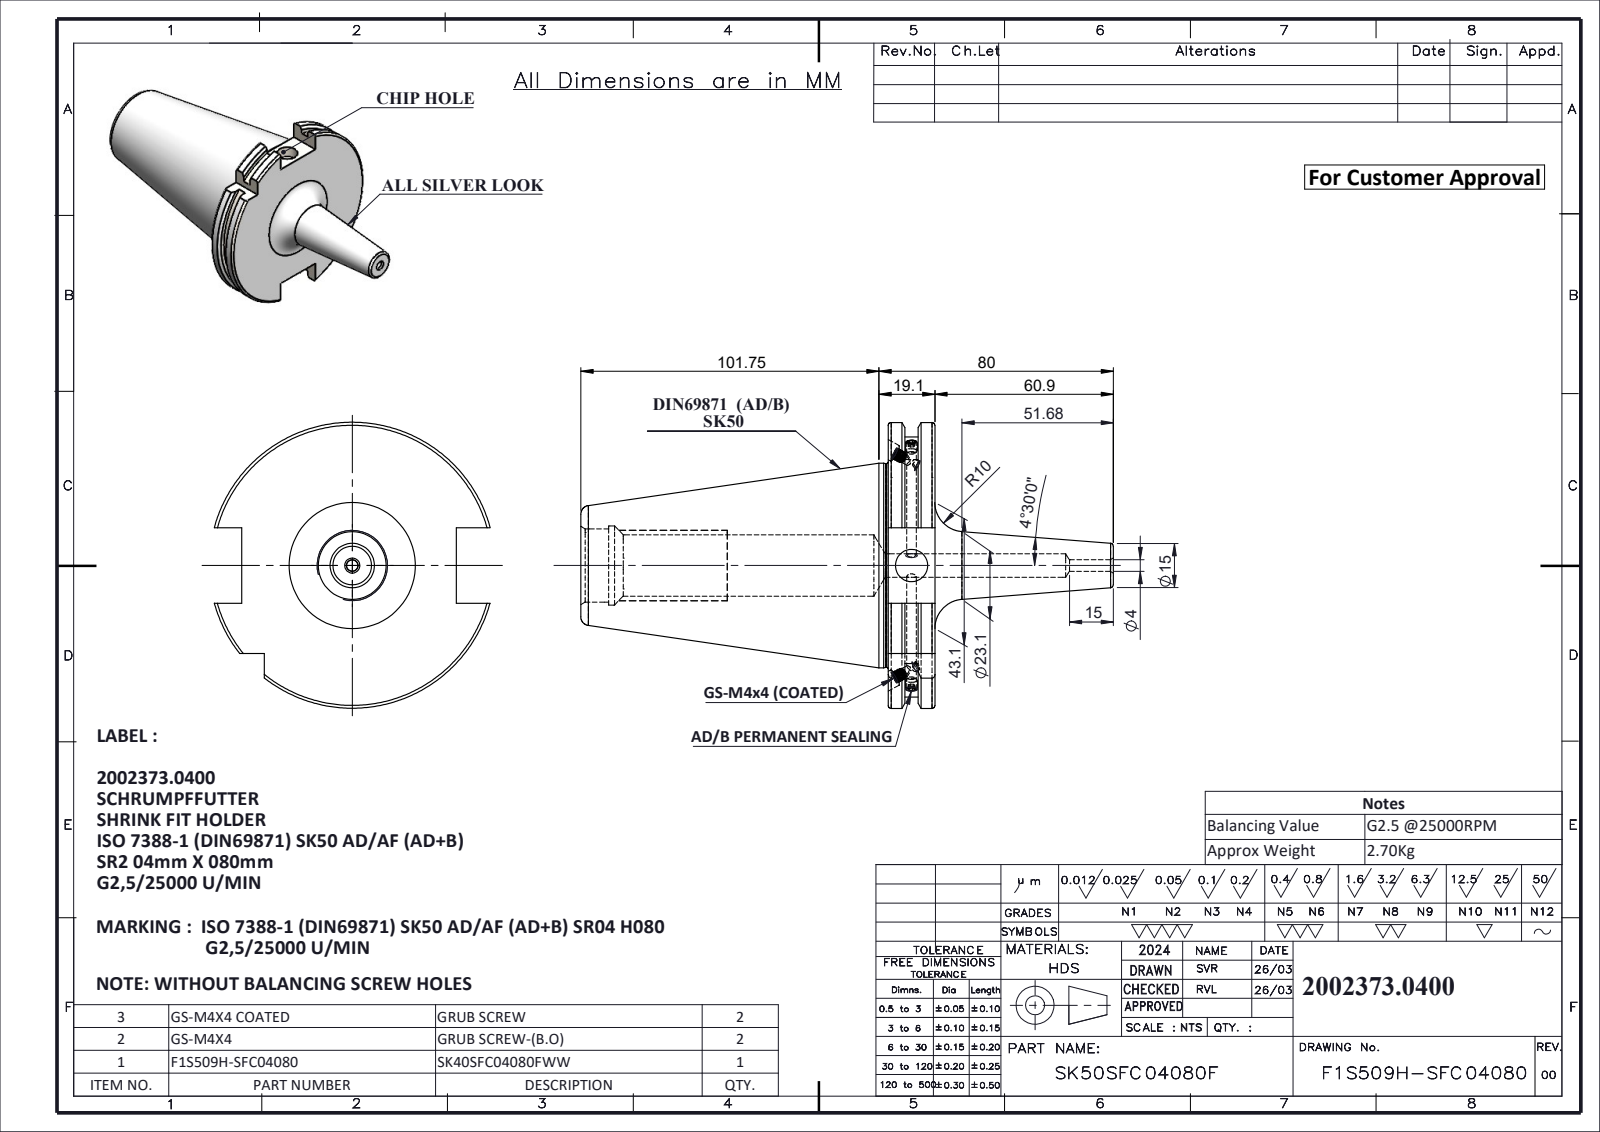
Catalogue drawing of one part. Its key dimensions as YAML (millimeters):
part_name: "GS-M4X4_DIN 913 - M4 x 4-N; GS-M4X4-COATING_DIN 913 - M4 x 4-N; SK50SFC04080FWW; F1S509H-SFC04080"
step_written_by: "SolidWorks 2024 (CONFIG_CONTROL_DESIGN)"
units: millimeters
bodies: {solids: 5, faces: 247, planar: 62, cylindrical: 71, other: 114}
overall_size: [181.75, 97.5, 94.05]
volume: 341869
surface_area: 49583
round_holes:
  - {diameter: 3.2, count: 2}
  - {diameter: 6, count: 2}
  - {diameter: 3.3, count: 1}
  - {diameter: 4, count: 1}
  - {diameter: 8, count: 1}
  - {diameter: 11, count: 1}
  - {diameter: 21, count: 1}
  - {diameter: 25, count: 1}
  - {diameter: 27, count: 1}
round_bosses_or_shafts:
  - {diameter: 4, count: 4}
  - {diameter: 2.9, count: 2}
  - {diameter: 69.85, count: 1}
  - {diameter: 69.45, count: 1}
partial_cylinders:
  - {radius: 44.9, count: 1}
  - {radius: 48.75, count: 1}
face_to_face_distances: [15.9, 5.65, 10.25, 10.14, 4.49, 5.76, 104.95, 110.6, 115.09, 120.85]
